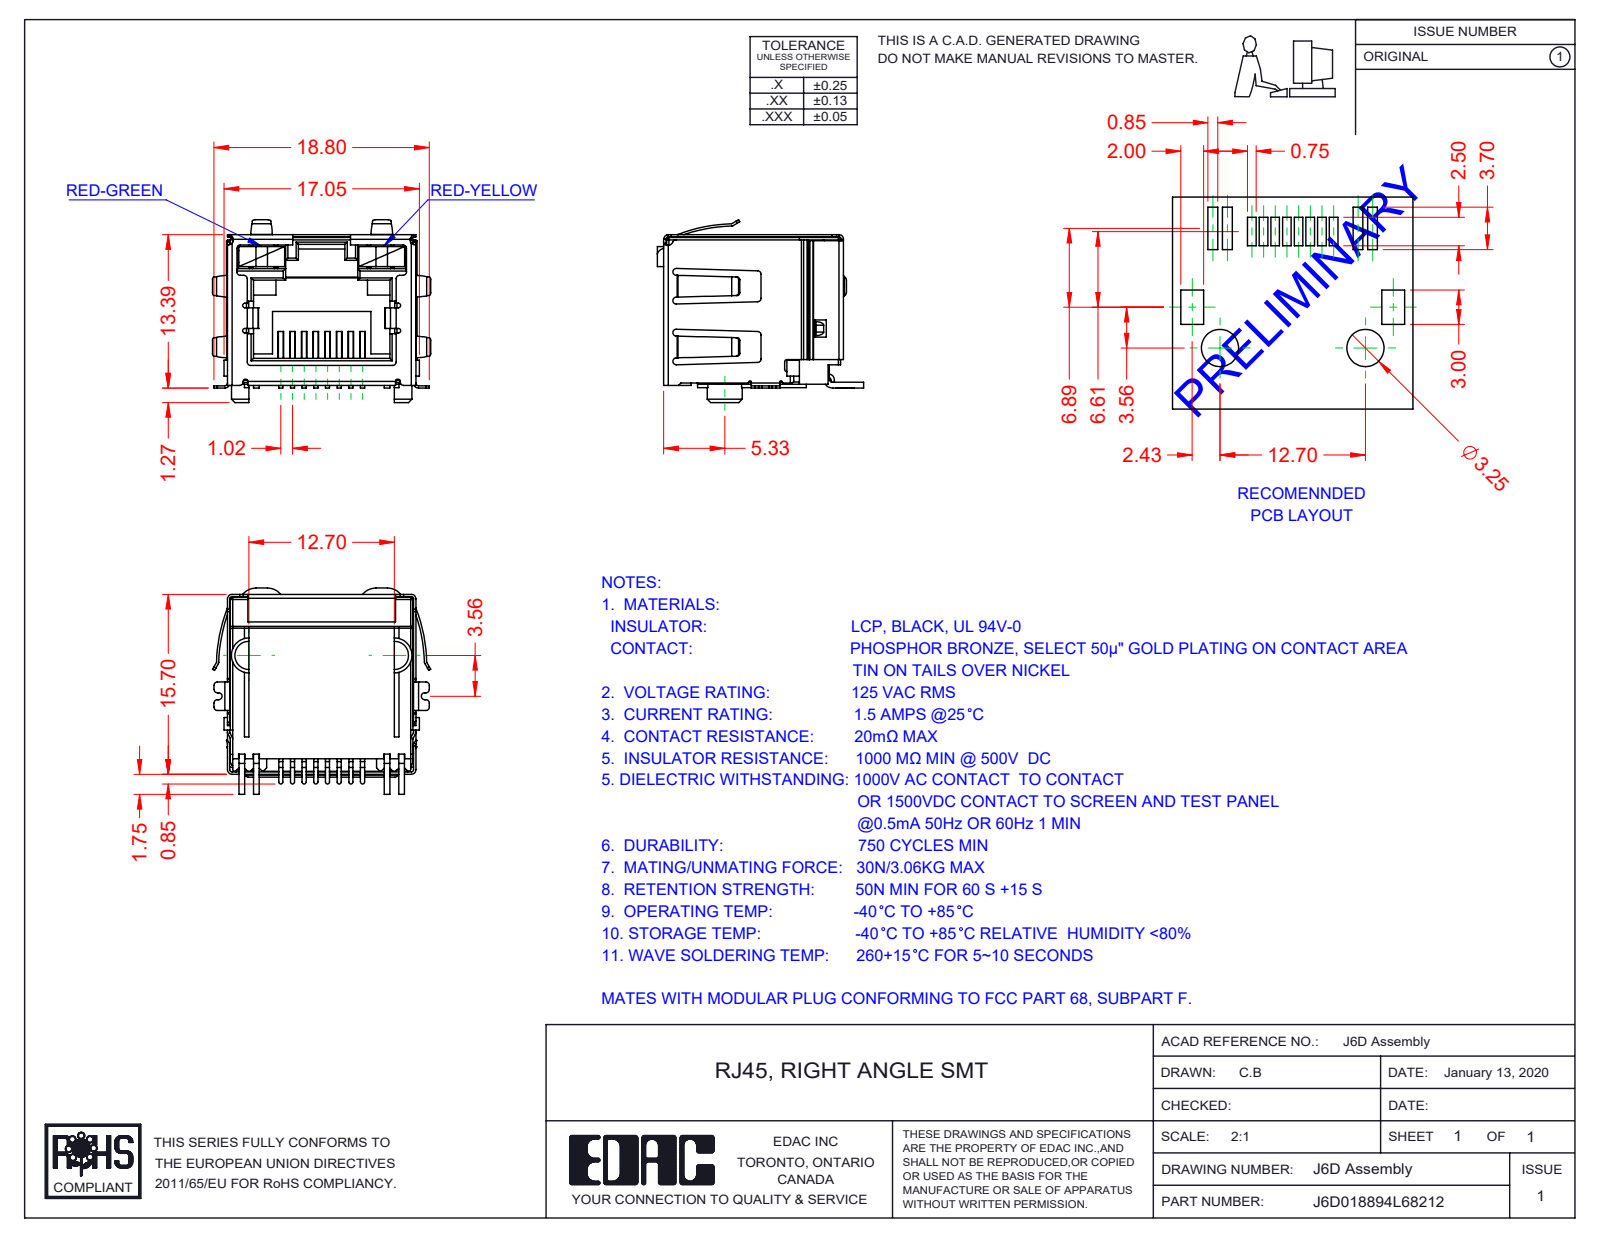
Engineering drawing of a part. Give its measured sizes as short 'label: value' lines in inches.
name: 6D LED LH_6-Red-Green; 6D Shield_LED - EMI; 6D Contacts; 6D LED RH_8-Red-Yellow (+2 more)
written by: SolidWorks 2016 (CONFIG_CONTROL_DESIGN)
unit: in
bodies: 12 solids, 1034 faces (703 planar, 286 cylindrical, 45 other)
size: 0.75 × 0.709 × 0.628
volume: 0.109 in³; area: 7.434 in²
rounds: 55× R0.012, 40× R0.008, 19× R0.016, 16× R0.01, 12× R0.004, 8× R0.006, 8× R0.007, 6× R0.02
face distances: 0.63, 0.638, 0.64, 0.089, 0.039, 0.628, 0.504, 0.018, 0.514, 0.417
